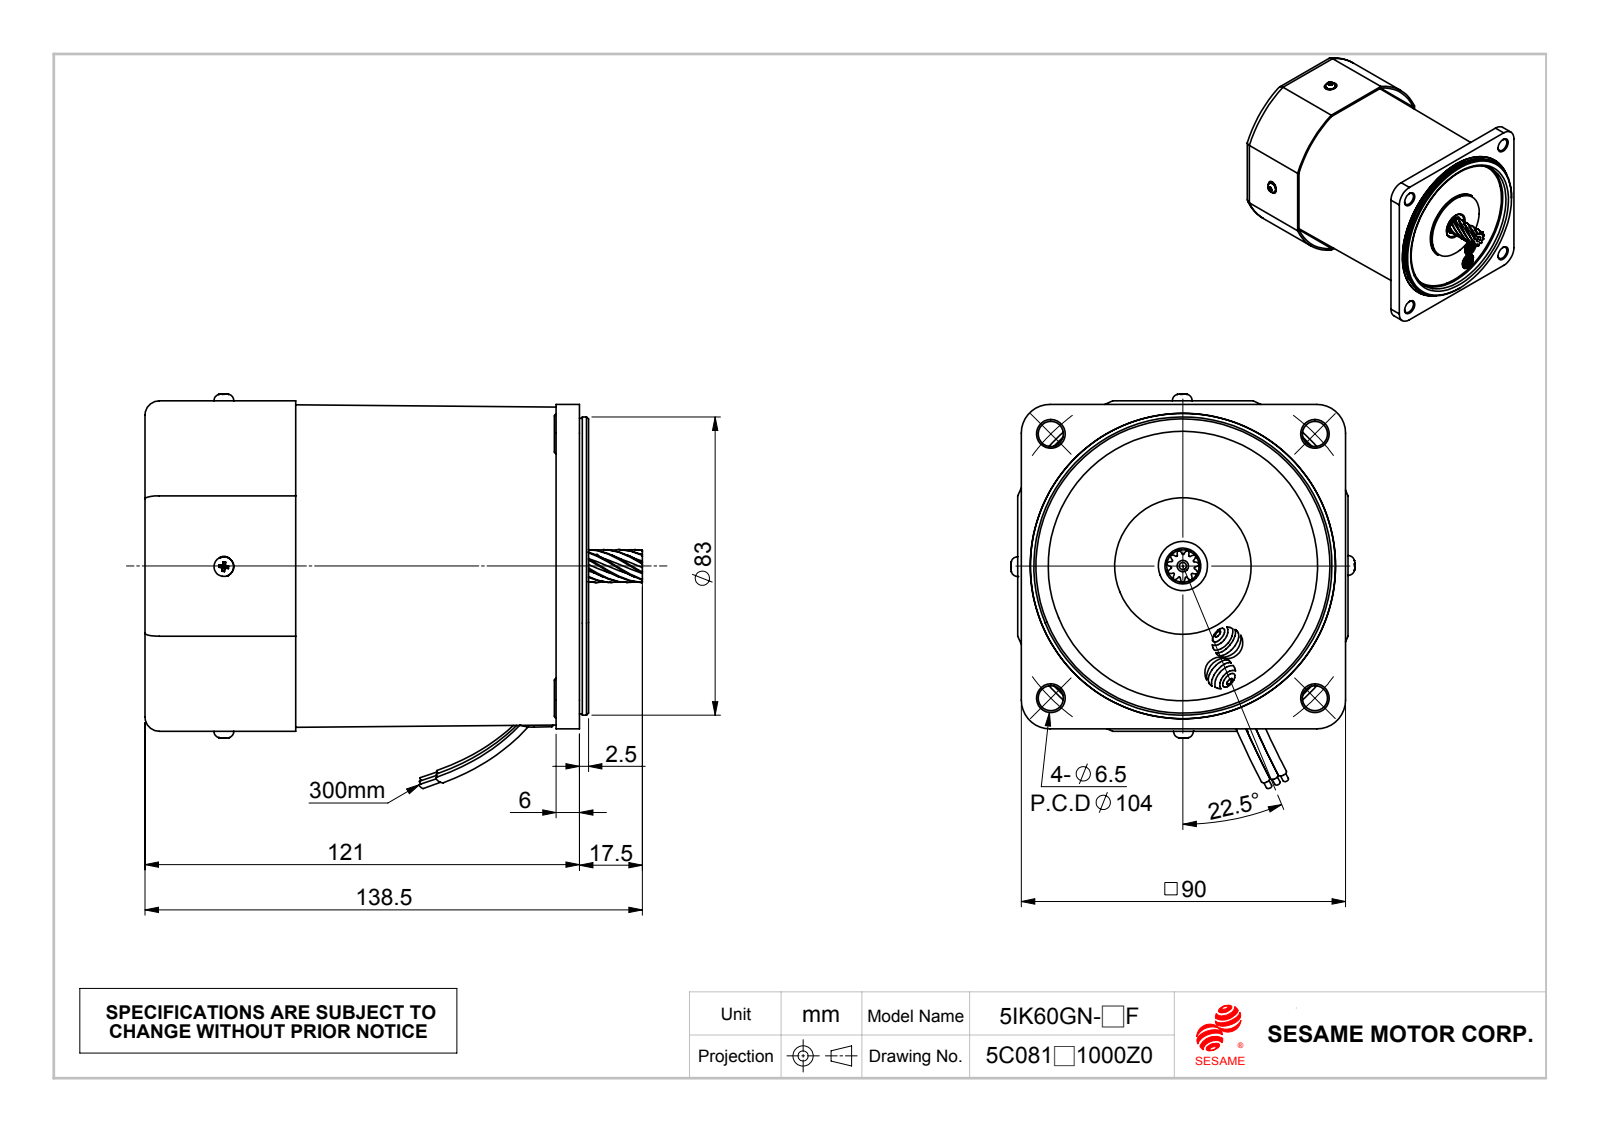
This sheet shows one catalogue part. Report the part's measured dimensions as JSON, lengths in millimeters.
{"part_name": "M560; 線扣; 風扇蓋FC-9042-21; 60GN", "step_written_by": "SolidWorks 2010 (CONFIG_CONTROL_DESIGN)", "units": "millimeters", "bodies": {"solids": 12, "faces": 717, "planar": 212, "cylindrical": 339, "other": 166}, "overall_size": [138.5, 109.84, 95.83], "volume_mm3": 682873, "surface_area_mm2": 101707, "round_holes": [[2.5, 5], [7, 4], [2, 1], [6.5, 1], [7.2, 1], [9.5, 1], [13.7, 1], [24, 1], [26, 1], [40, 1], [54, 1], [58.1, 1]], "round_bosses_or_shafts": [[5.5, 4], [3, 4], [84.22, 1], [83, 1], [82.2, 1], [47, 1], [38, 1], [31, 1]], "partial_cylinders_radius": [[0.3, 16], [0.25, 8], [0.78, 8], [1, 8], [1.5, 8], [1.66, 8], [2.92, 8], [0.2, 4]], "face_to_face_distances": [1, 118.5, 91, 16, 102.5, 0.9, 118.4, 119.4, 117.5, 119.5], "hole_center_spacings": [52, 73.54, 104]}
